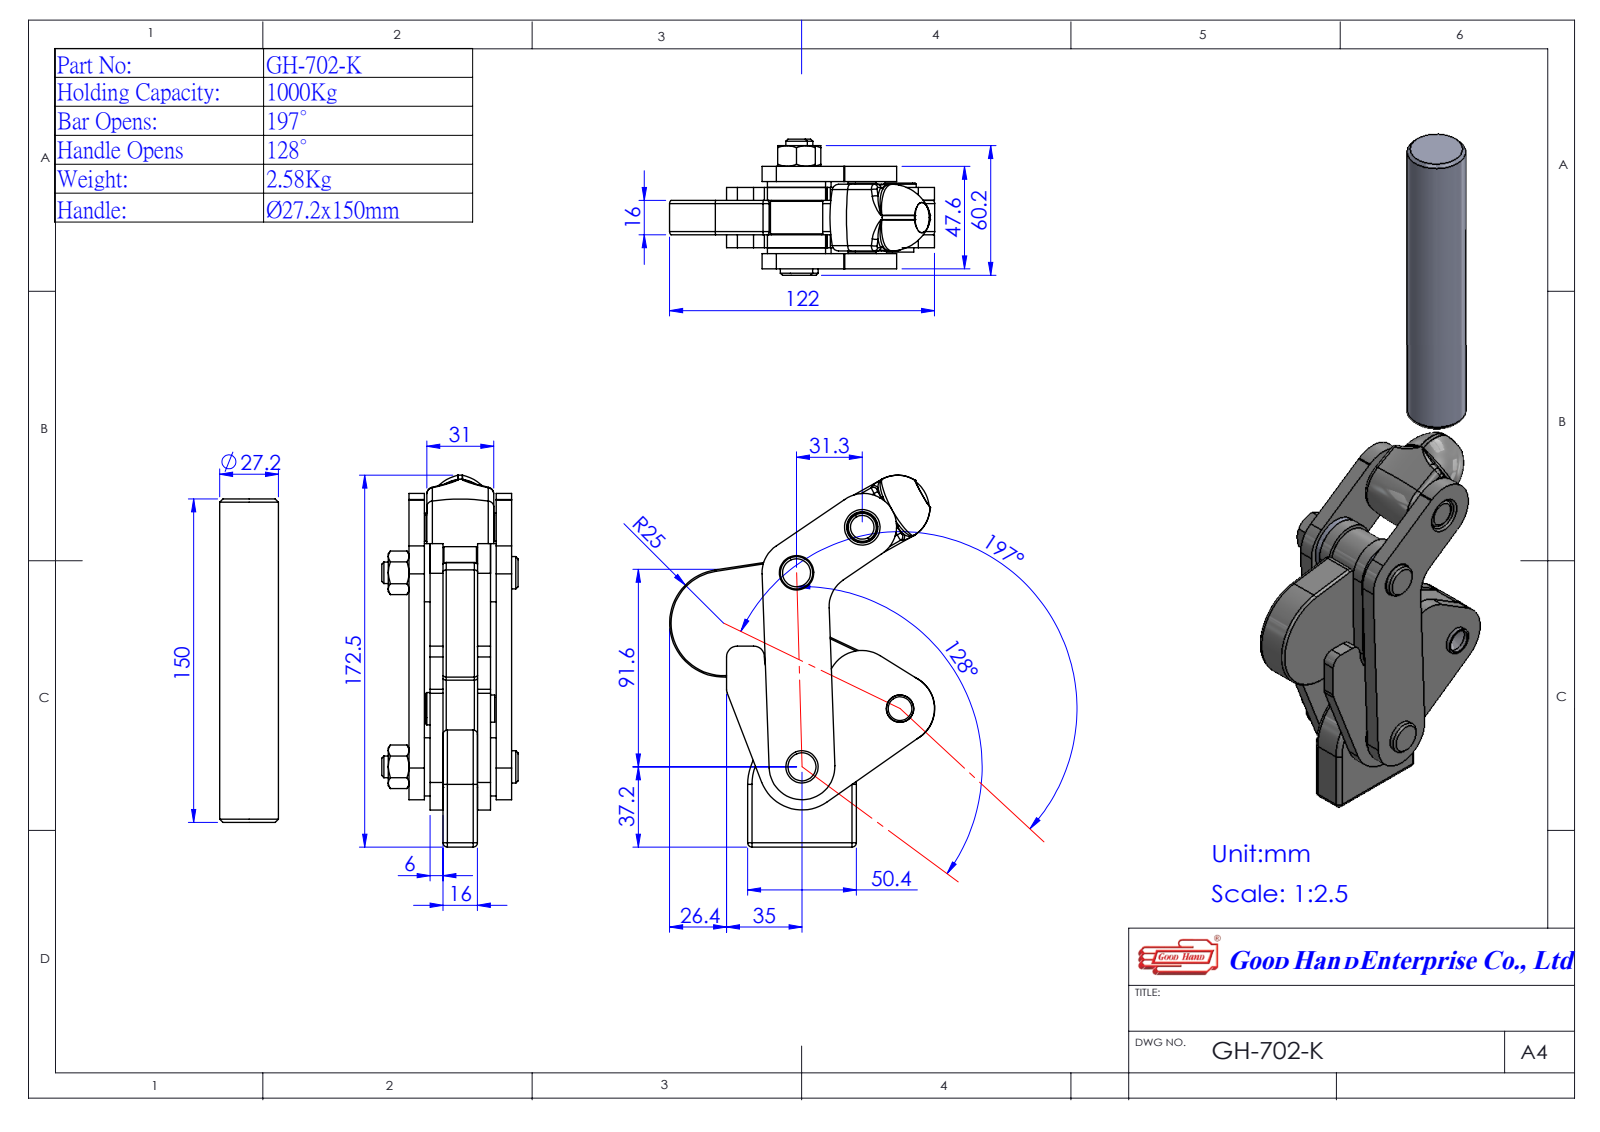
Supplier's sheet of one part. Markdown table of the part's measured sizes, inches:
| quantity | value |
| --- | --- |
| part name | GH-702-K(簡化); Group4^GH-702-K(簡化); 3702K08-1^GH-702-K(簡化); 3701K26-1^GH-702-K(簡化) (+4 more) |
| STEP written by | SolidWorks 2016 (AUTOMOTIVE_DESIGN) |
| units | inches |
| bodies | 7 solids, 260 faces (95 planar, 112 cylindrical, 53 other) |
| overall size | 12.824 × 4.832 × 2.488 |
| volume | 20.7 in³ |
| surface area | 180.5 in² |
| round holes (diameter × count) | 0.498 × 2, 0.512 × 1, 0.551 × 1, 0.854 × 1 |
| round bosses / shafts (diameter × count) | 0.591 × 4, 1.063 × 2, 0.498 × 2, 0.394 × 2, 1.071 × 1, 0.957 × 1 |
| partial cylindrical surfaces (radius × count) | 0.984 × 4, 0.197 × 3, 0.591 × 3, 0.63 × 3, 0.039 × 2, 3.209 × 2, 0.098 × 1, 0.236 × 1 |
| main face-to-face distances | 0.343, 0.972, 0.63, 0.106, 1.209, 0.236, 0.866, 0.386, 0.28, 0.622 |
| hole center spacings | 1.46, 3.545, 4.51 |
